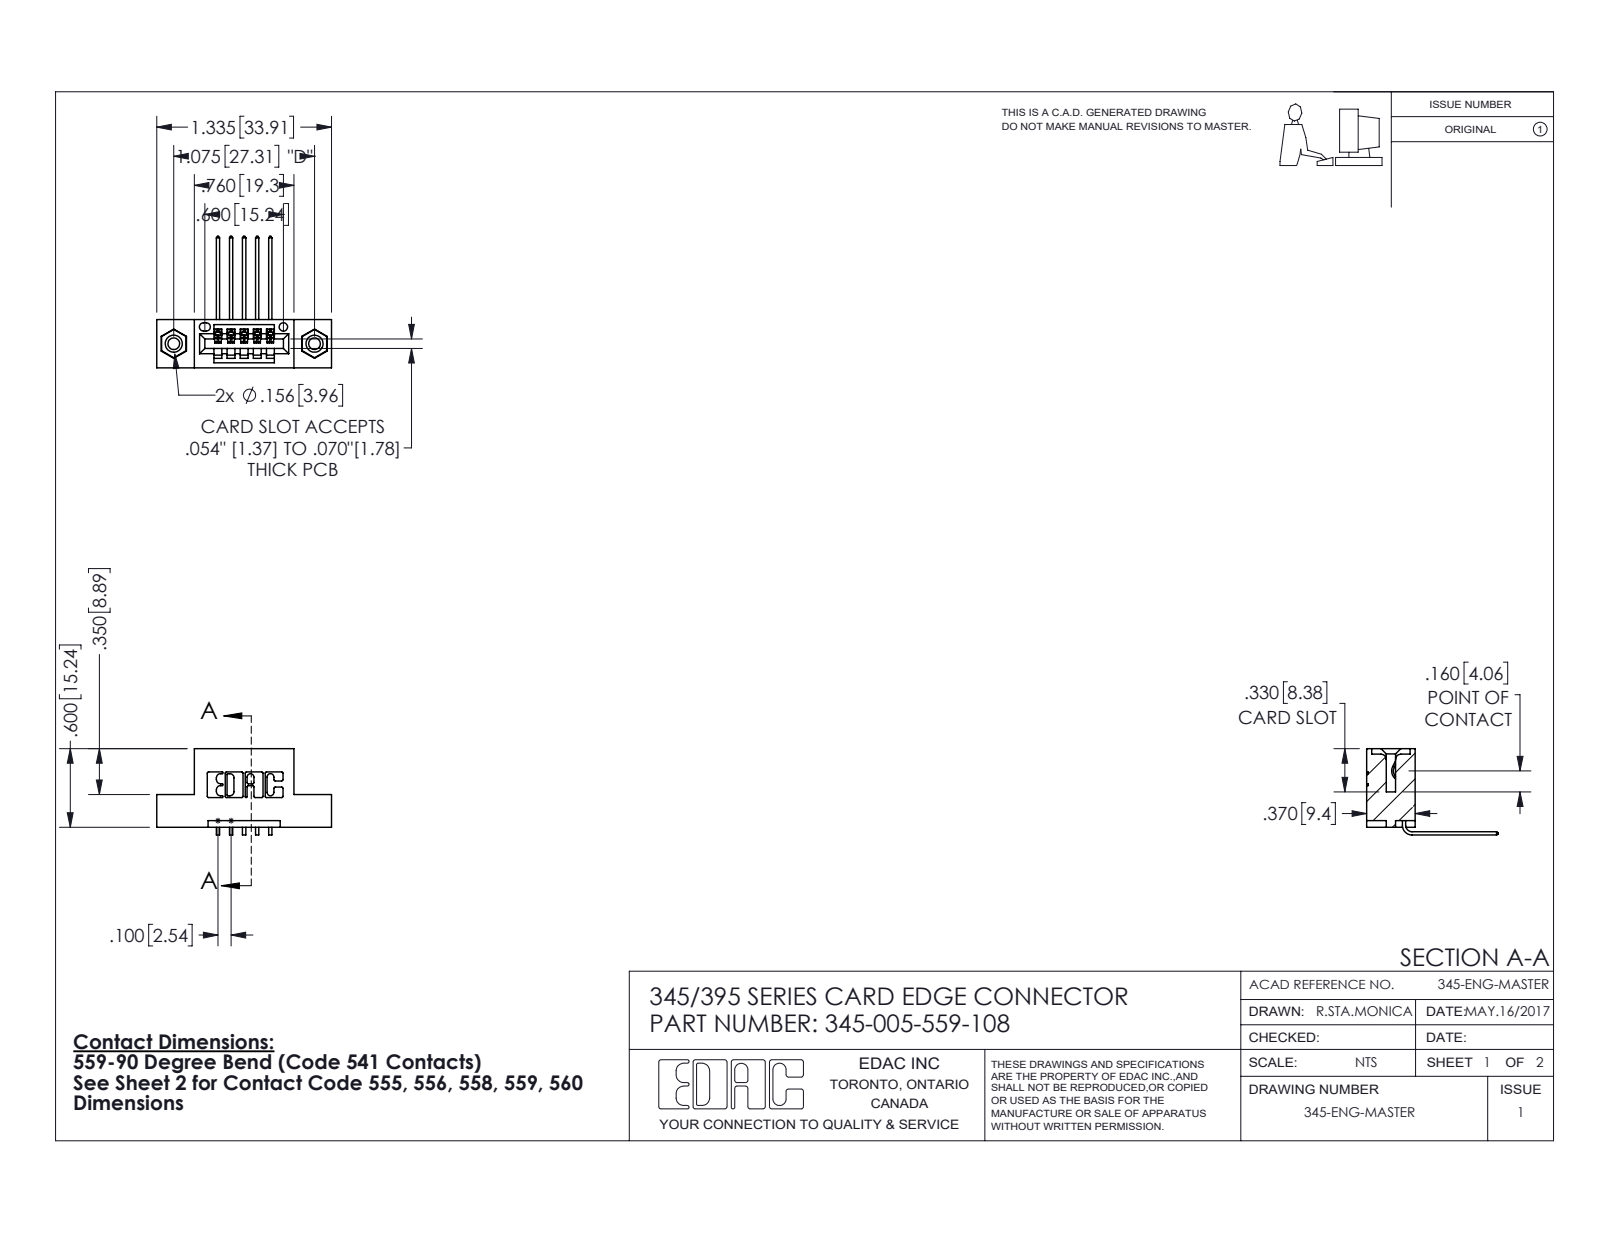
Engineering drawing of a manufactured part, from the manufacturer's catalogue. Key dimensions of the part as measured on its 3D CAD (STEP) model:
Part name (STEP PRODUCT): 345-250-001_345-250-003-102; 345-292-001_558 559 Tail - 1; 345-005-559-108; 345 Part_Flush Mounting Lugs - 0.156 Dia-TI
STEP written by: SolidWorks 2016 (CONFIG_CONTROL_DESIGN)
Units: inches
Bodies: 8 solids, 486 faces (322 planar, 148 cylindrical, 16 other)
Overall size (bounding box): 1.335 × 1.005 × 0.659
Volume: 0.179 in³ · Surface area: 5.433 in²
Round holes (diameter × count): ⌀0.089 ×2, ⌀0.125 ×2, ⌀0.156 ×2, ⌀0.064 ×1
Round bosses / shafts (diameter × count): ⌀0.155 ×2
Partial cylindrical surfaces — rounded edges, fillets, slot ends (radius × count): R0.01 ×22, R0.006 ×10, R0.007 ×6, R0.031 ×6, R0.026 ×3, R0.031 ×2, R0.04 ×2, R0.014 ×1
Main face-to-face distances: 0.2, 0.37, 0.1, 0.072, 0.298, 0.35, 0.25, 0.06, 0.098, 0.272
Hole centre spacings: 0.27, 0.847, 1.075
